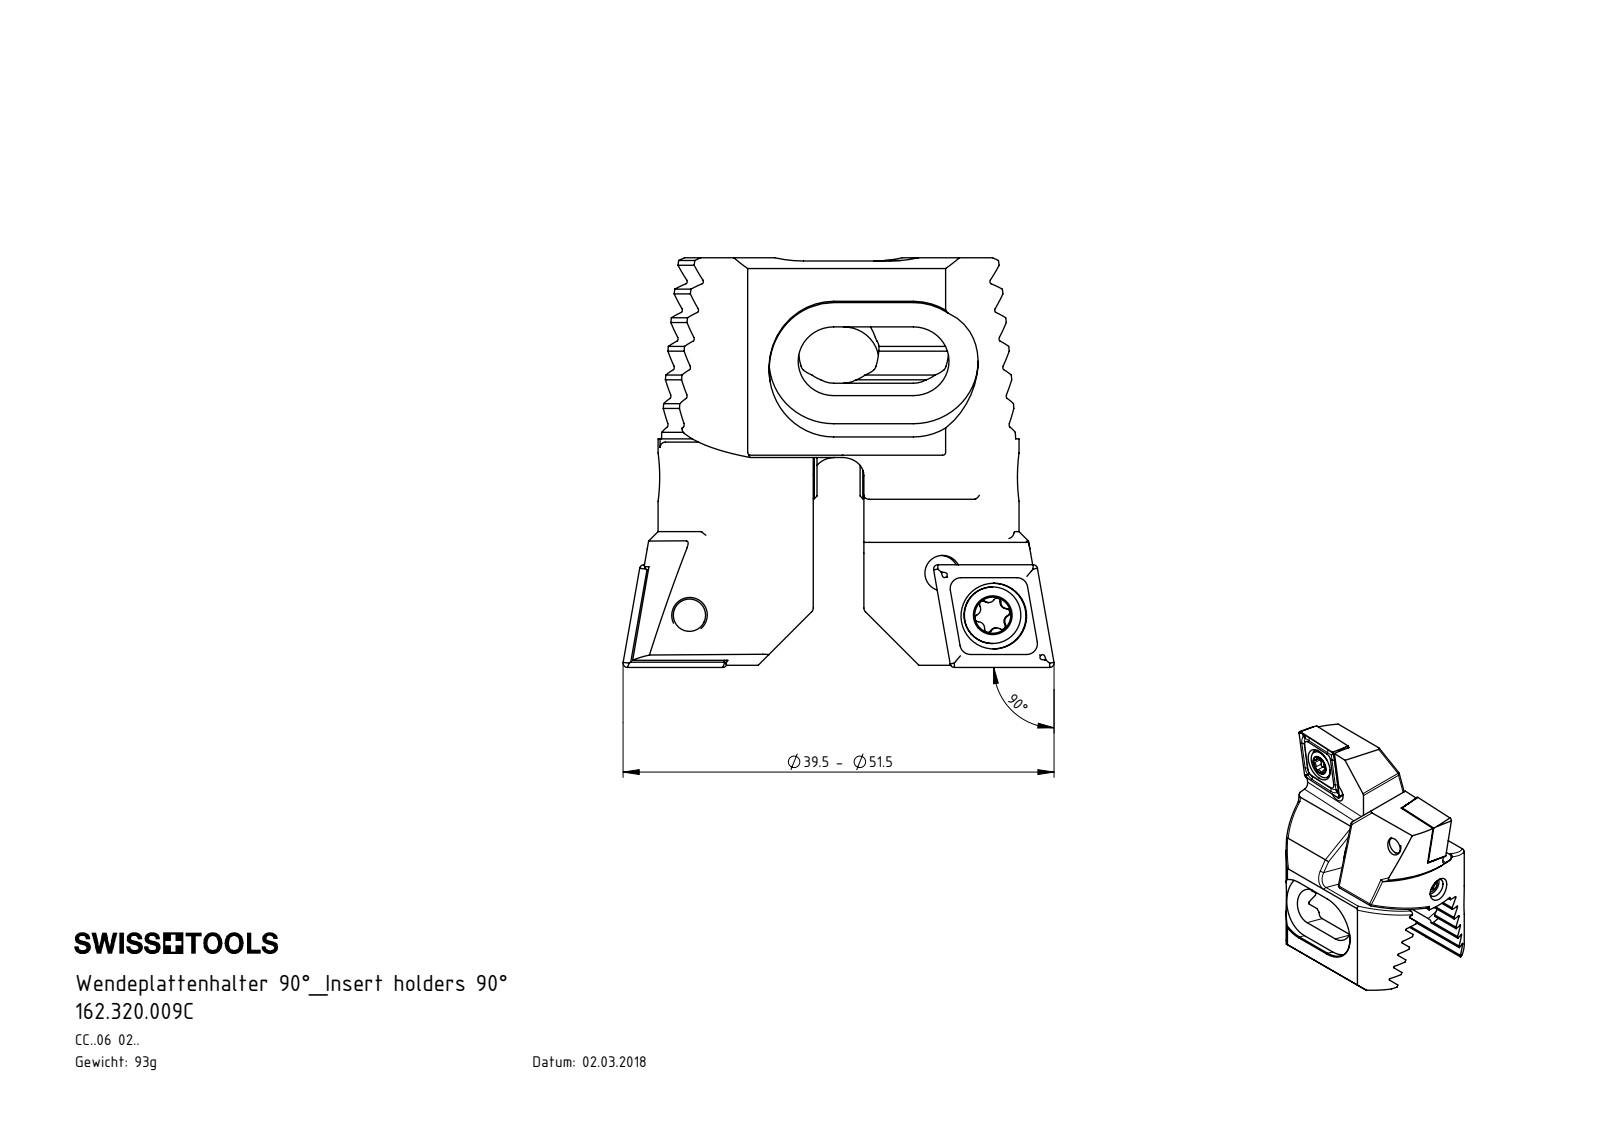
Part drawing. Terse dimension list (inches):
name: Z32-xxx.001.021_B; Z32-ER3.001.013_A; CCMT09T304; 162.320.009C (+1 more)
written by: SolidWorks 2017 (CONFIG_CONTROL_DESIGN)
unit: in
bodies: 8 solids, 646 faces (294 planar, 136 cylindrical, 216 other)
size: 1.575 × 1.496 × 1.031
volume: 0.724 in³; area: 12.8 in²
holes: 4× ⌀0.13, 2× ⌀0.063, 2× ⌀0.173, 2× ⌀0.24, 1× ⌀0.079, 1× ⌀0.138
bosses: 3× ⌀0.157, 2× ⌀0.207
rounds: 16× R0.02, 12× R0.008, 12× R0.013, 12× R0.023, 4× R0.079, 4× R0.13, 4× R0.236, 4× R0.472
face distances: 0.094, 0.187, 0.375, 0.281, 0.193, 0.469, 0.281, 0.05, 0.188, 0.094
hole spacings: 0.239, 0.244, 0.354, 0.954, 0.958, 1.128, 0.684, 0.759
